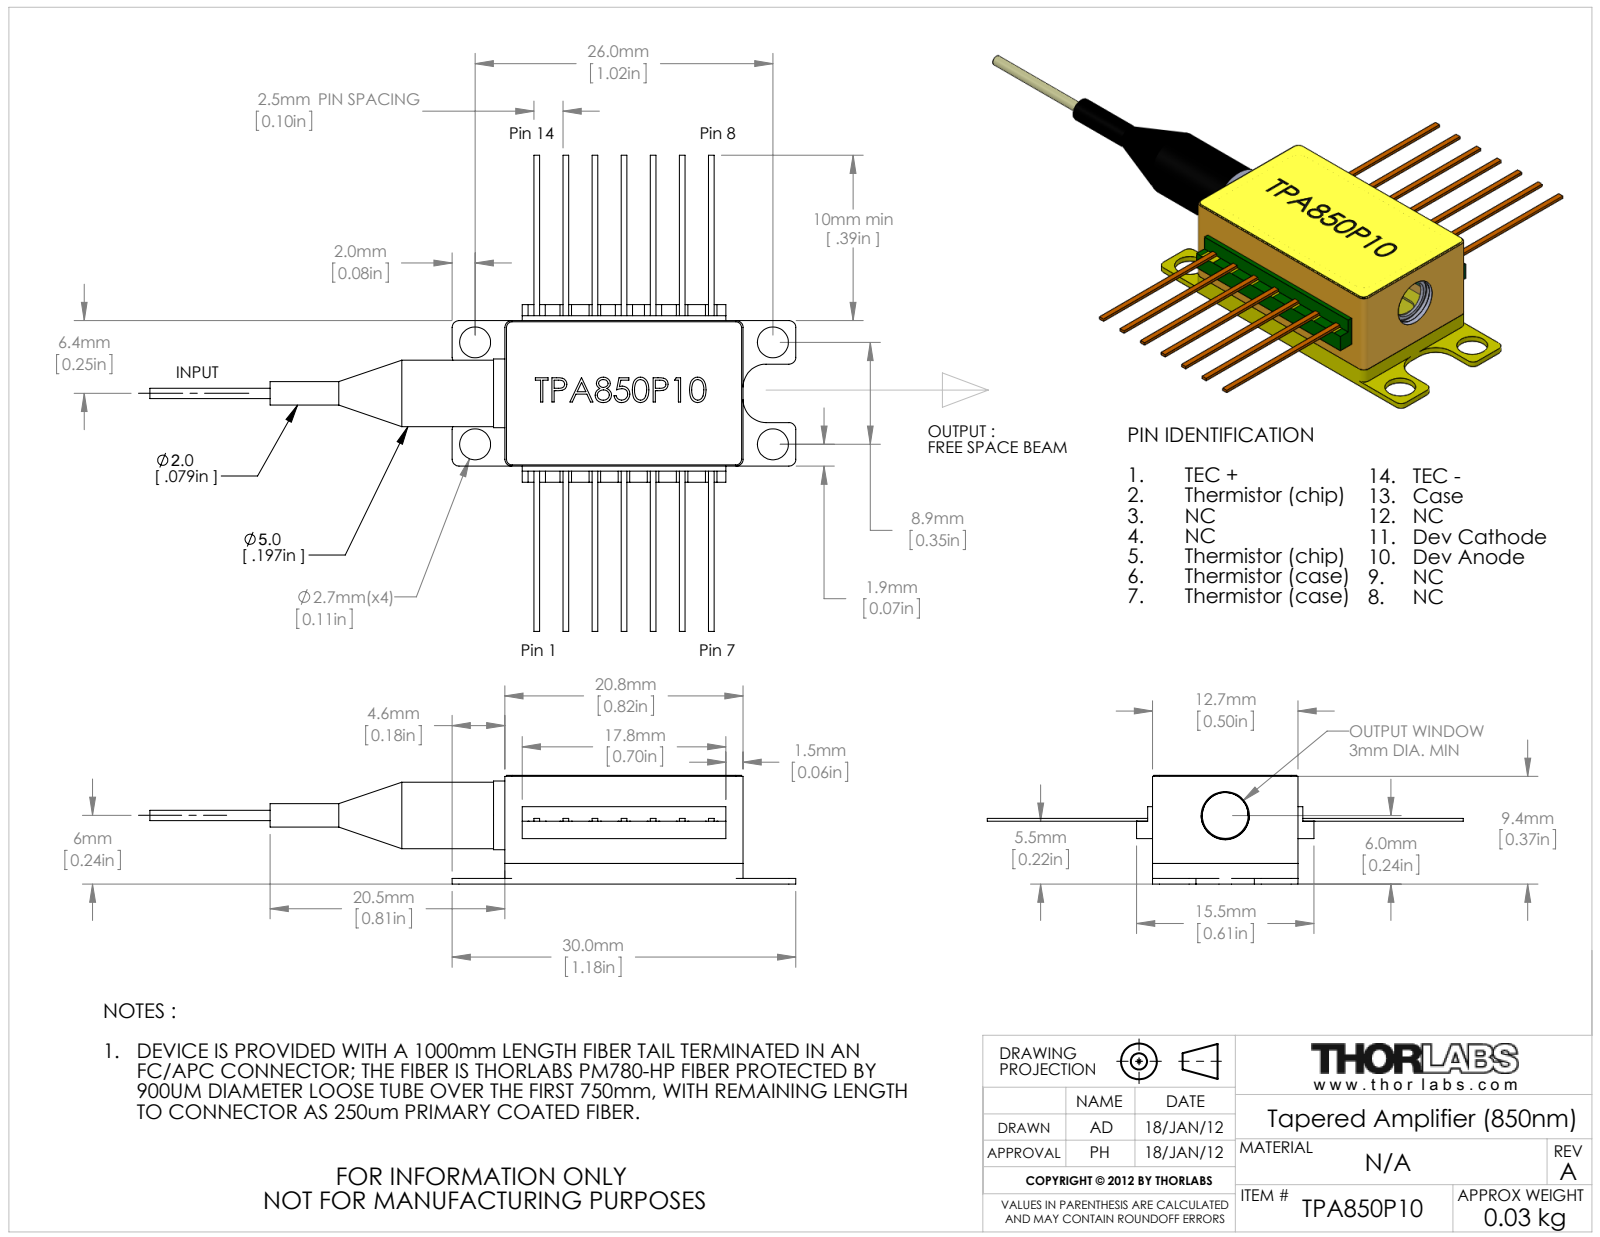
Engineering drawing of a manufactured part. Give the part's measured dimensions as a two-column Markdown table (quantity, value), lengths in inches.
| quantity | value |
| --- | --- |
| part name | 23401-E0W; 32025-000 Lid (Labelled for TPA850P10); TPA 14pin butterfly package |
| STEP written by | SolidWorks 2011 (AUTOMOTIVE_DESIGN) |
| units | inches |
| bodies | 1 solid, 409 faces (278 planar, 70 cylindrical, 61 other) |
| overall size | 2.22 × 1.636 × 0.374 |
| volume | 0.004 in³ |
| surface area | 5.194 in² |
| round holes (diameter × count) | 0.106 × 4, 0.043 × 1, 0.082 × 1, 0.134 × 1, 0.165 × 1 |
| round bosses / shafts (diameter × count) | 0.236 × 1, 0.228 × 1, 0.157 × 1, 0.08 × 1, 0.079 × 1, 0.035 × 1 |
| partial cylindrical surfaces (radius × count) | 0.024 × 12, 0.039 × 12, 0.008 × 4, 0.02 × 4, 0.079 × 4, 0.005 × 2 |
| main face-to-face distances | 0.039, 0.374, 0.299, 0.362, 0.461, 0.5, 0.071, 0.291, 0.303, 0.37 |
| hole center spacings | 0.35, 1.024, 1.082 |
